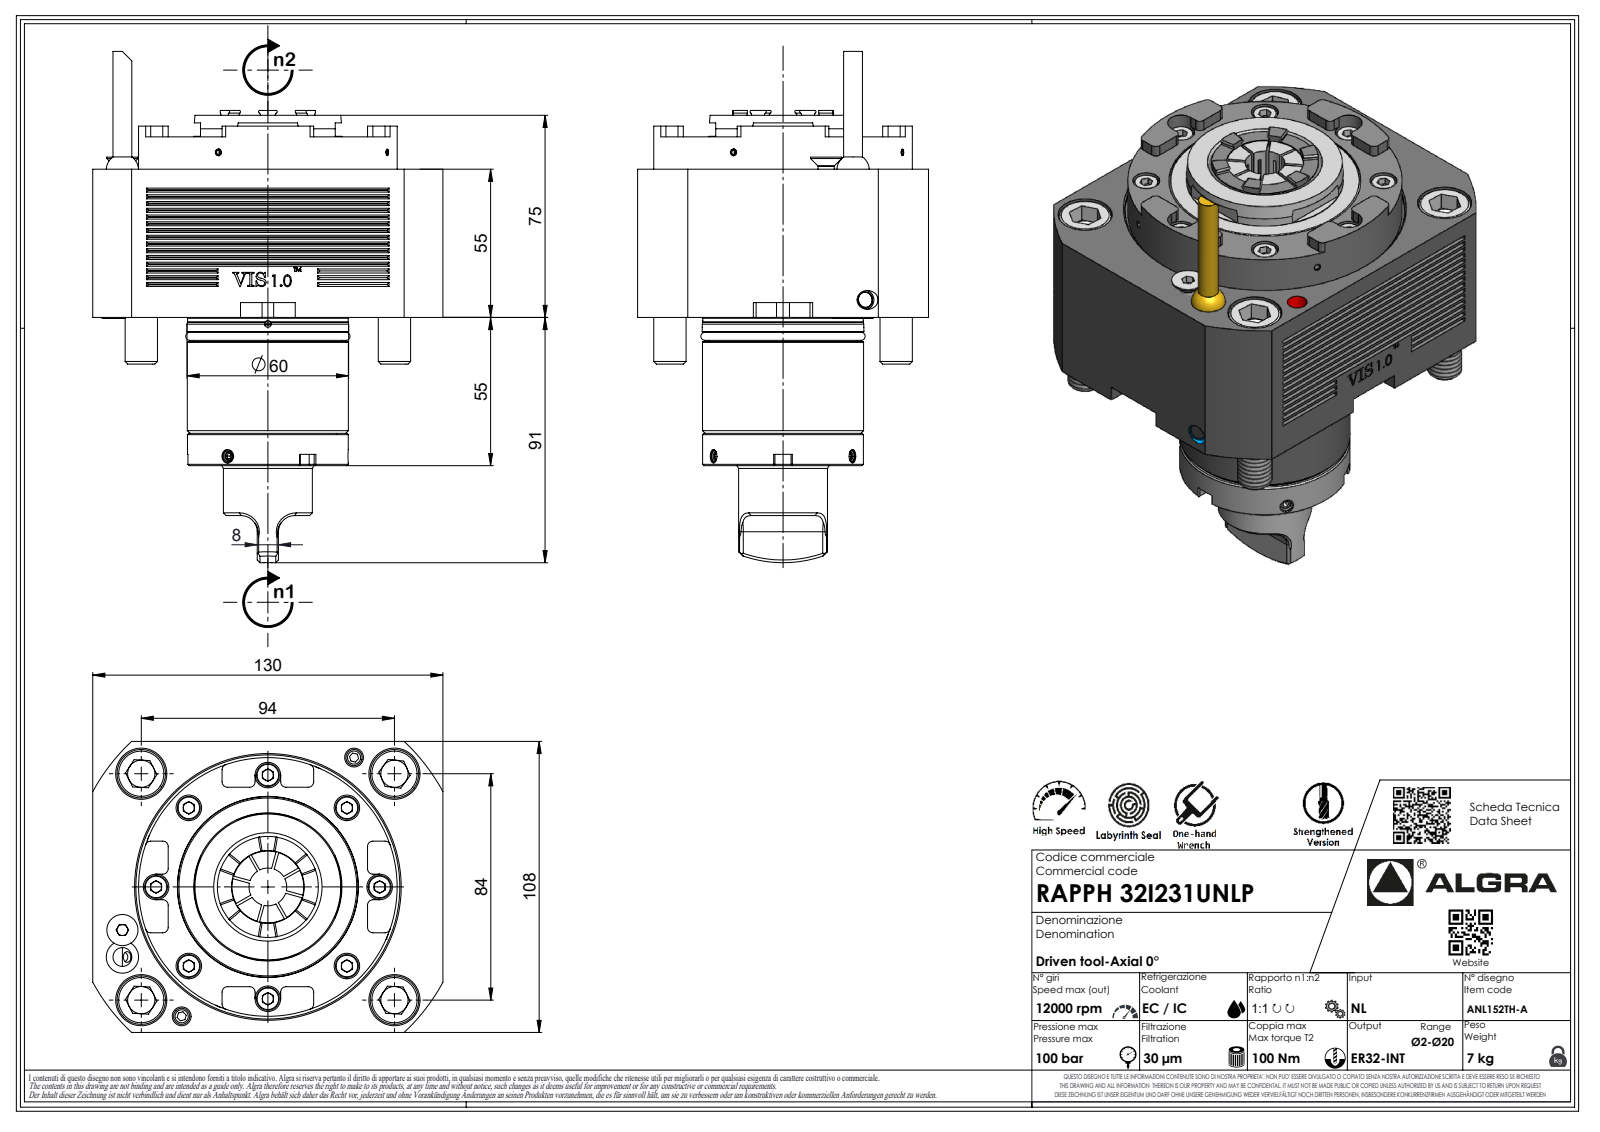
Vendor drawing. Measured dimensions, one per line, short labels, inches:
name: RAPPH32I231UNLP
written by: SolidWorks 2023 (AUTOMOTIVE_DESIGN)
unit: in
bodies: 1 solid, 577 faces (330 planar, 104 cylindrical, 143 other)
size: 7.469 × 5.118 × 4.252
volume: 62.79 in³; area: 122.3 in²
holes: 1× ⌀0.071, 1× ⌀0.083, 1× ⌀0.157
bosses: 4× ⌀0.472, 1× ⌀3.78, 1× ⌀2.362, 1× ⌀2.354, 1× ⌀2.35, 1× ⌀2.346, 1× ⌀2.173, 1× ⌀2.165
rounds: 25× R0.079, 8× R0.315, 7× R0.013, 7× R0.02, 7× R0.146, 6× R0.236, 4× R0.187, 3× R0.118
face distances: 2.165, 4.252, 0.472, 2.638, 5.118, 4.35, 0.787, 0.315, 2.953, 0.157
